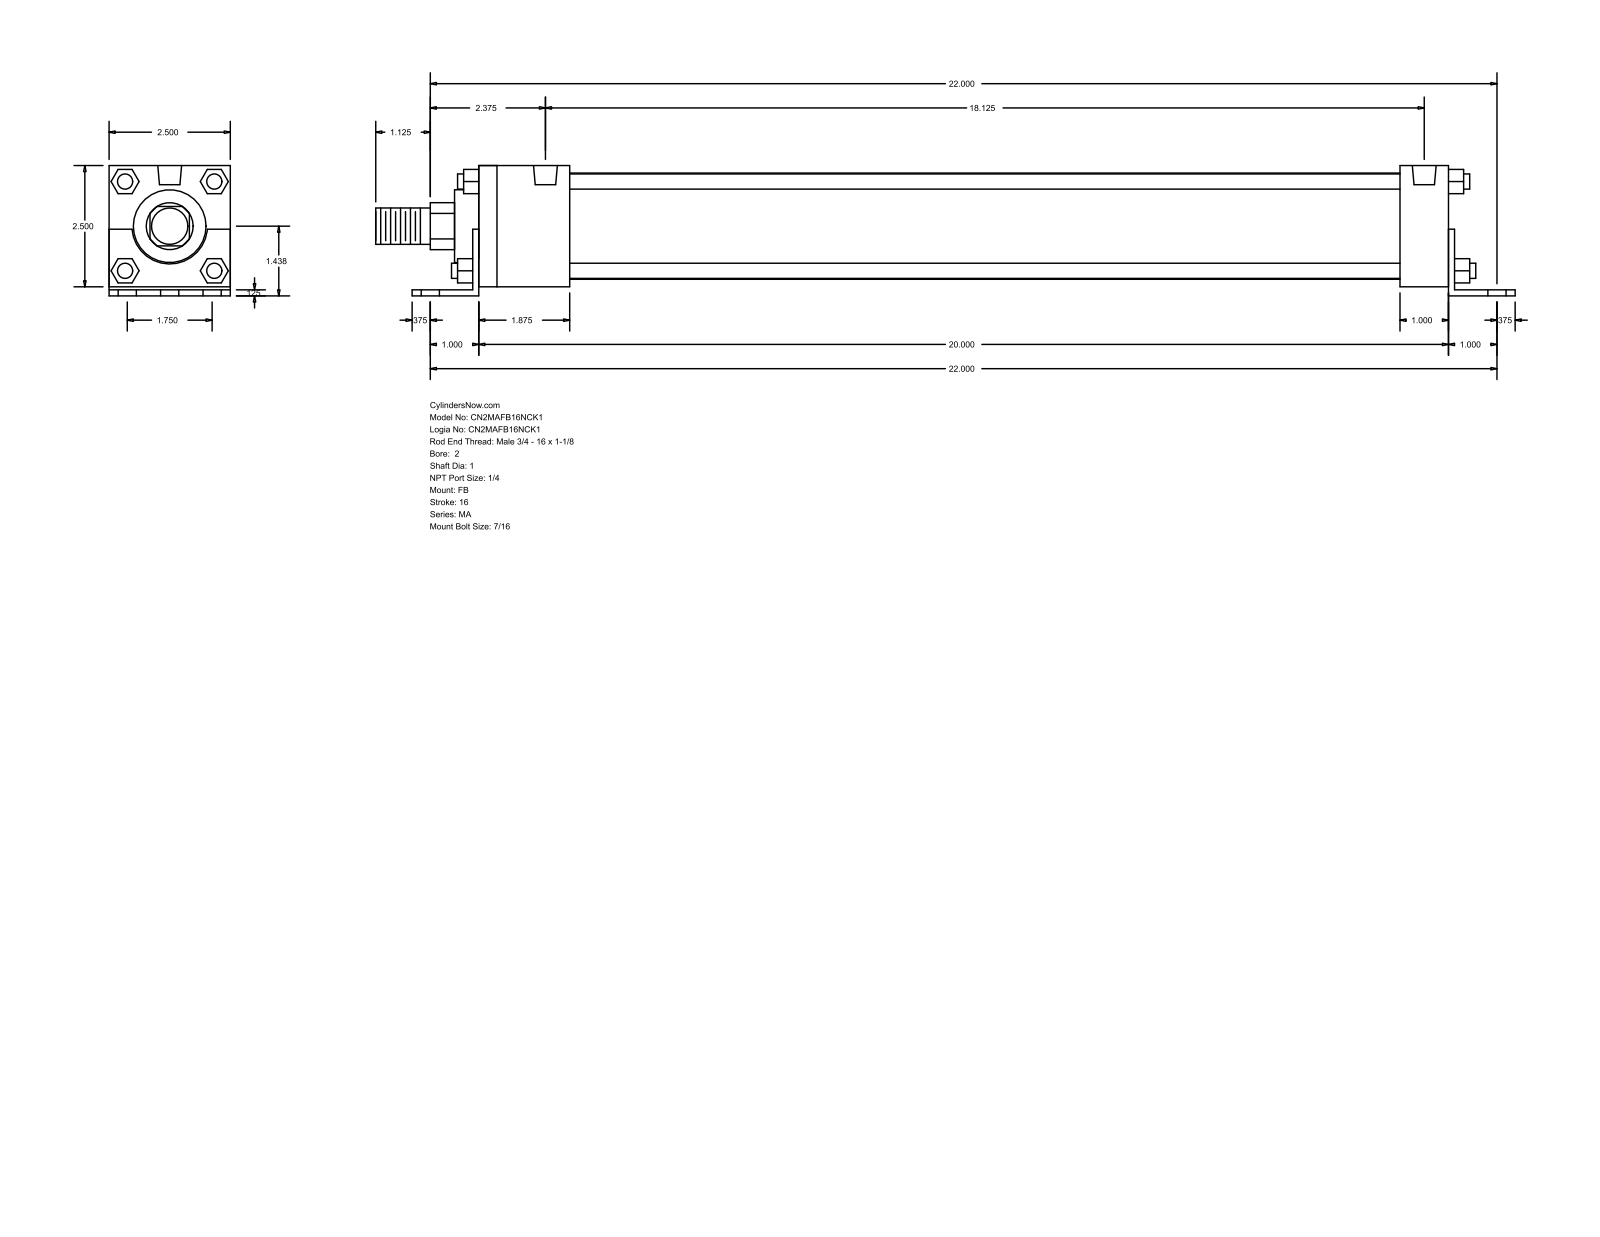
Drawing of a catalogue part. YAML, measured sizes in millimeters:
part_name: "MA_FB__0200_1"
step_written_by: "GSSL Pune (CONFIG_CONTROL_DESIGN)"
units: millimeters
bodies: {solids: 0, faces: 140, planar: 105, cylindrical: 35, other: 0}
overall_size: [596.9, 68.26, 63.5]
round_holes:
  - {diameter: 11.11, count: 6}
  - {diameter: 7.94, count: 4}
  - {diameter: 12.49, count: 2}
round_bosses_or_shafts:
  - {diameter: 7.94, count: 4}
  - {diameter: 55.63, count: 1}
  - {diameter: 38.1, count: 1}
  - {diameter: 25.4, count: 1}
  - {diameter: 19.05, count: 1}
partial_cylinders:
  - {radius: 12.29, count: 1}
  - {radius: 19.81, count: 1}
face_to_face_distances: [63.5, 3.17, 4.76, 68.26, 1.59, 65.09, 12.7, 3.18, 508, 511.18]
hole_center_spacings: [22.23, 559.24, 558.8, 44.11, 44.46, 64.3, 460.37, 498.97]
